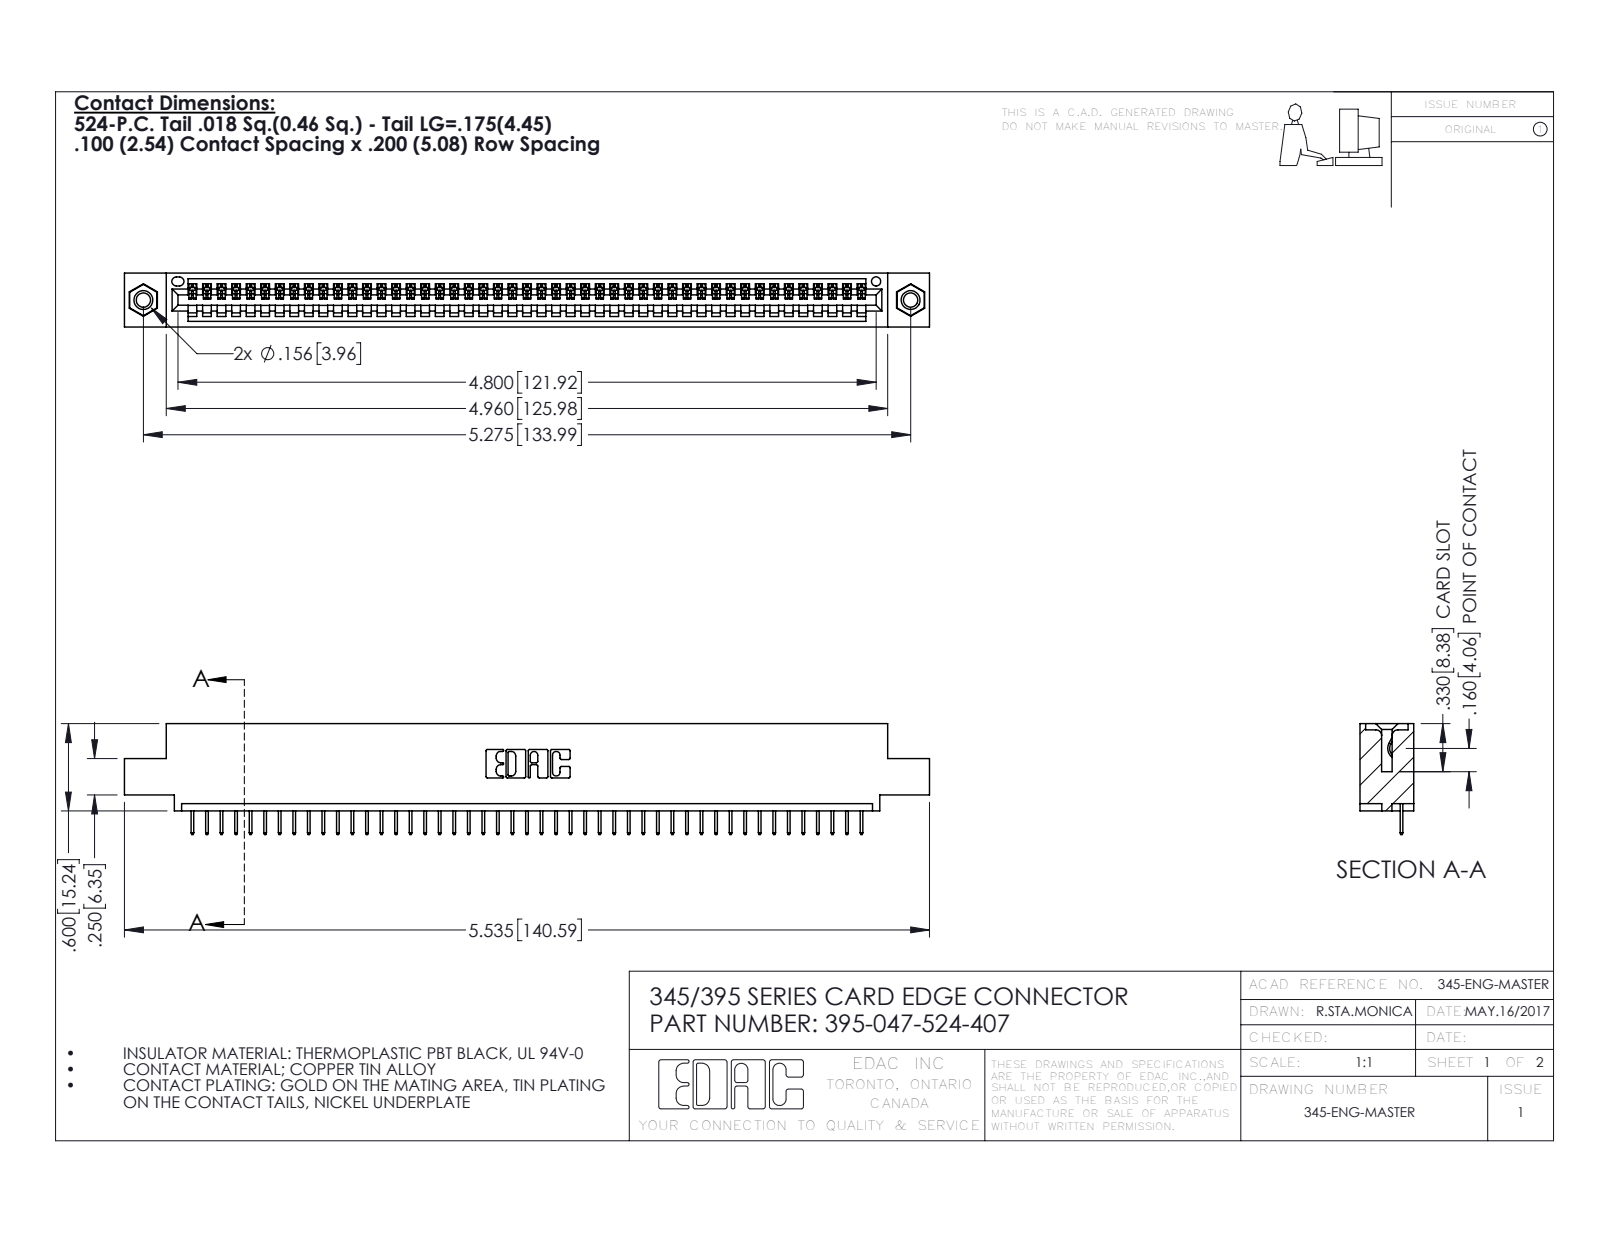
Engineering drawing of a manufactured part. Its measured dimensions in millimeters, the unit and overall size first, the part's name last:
Units: millimetres
Overall size (bounding box): 140.6 × 19.4 × 9.4
Round holes (diameter × count): ⌀2.5 ×2, ⌀3.2 ×2, ⌀4 ×2, ⌀1.6 ×1
Round bosses / shafts (diameter × count): ⌀3.9 ×2
Partial cylindrical surfaces — rounded edges, fillets, slot ends (radius × count): R0.2 ×94, R0.3 ×22, R0.2 ×6, R0.8 ×6, R0.7 ×3, R0.8 ×2, R1 ×2, R0.4 ×1
Main face-to-face distances: 1.8, 7.6, 9.4, 5.1, 2.5, 6.9, 0.6, 5.7, 1.8, 3.8
Hole centre spacings: 6.9, 128, 134
Volume: 13 100 mm³ · Surface area: 17 030 mm²
Bodies: 50 solids, 3104 faces (2278 planar, 810 cylindrical, 16 other)
Part name (STEP PRODUCT): 345-250-001_345-250-005-103; 345 Part_0.110 Offset - 0.156 Dia-TI; 345-292-001_345-293-124; 395-047-524-407
STEP written by: SolidWorks 2016 (CONFIG_CONTROL_DESIGN)
